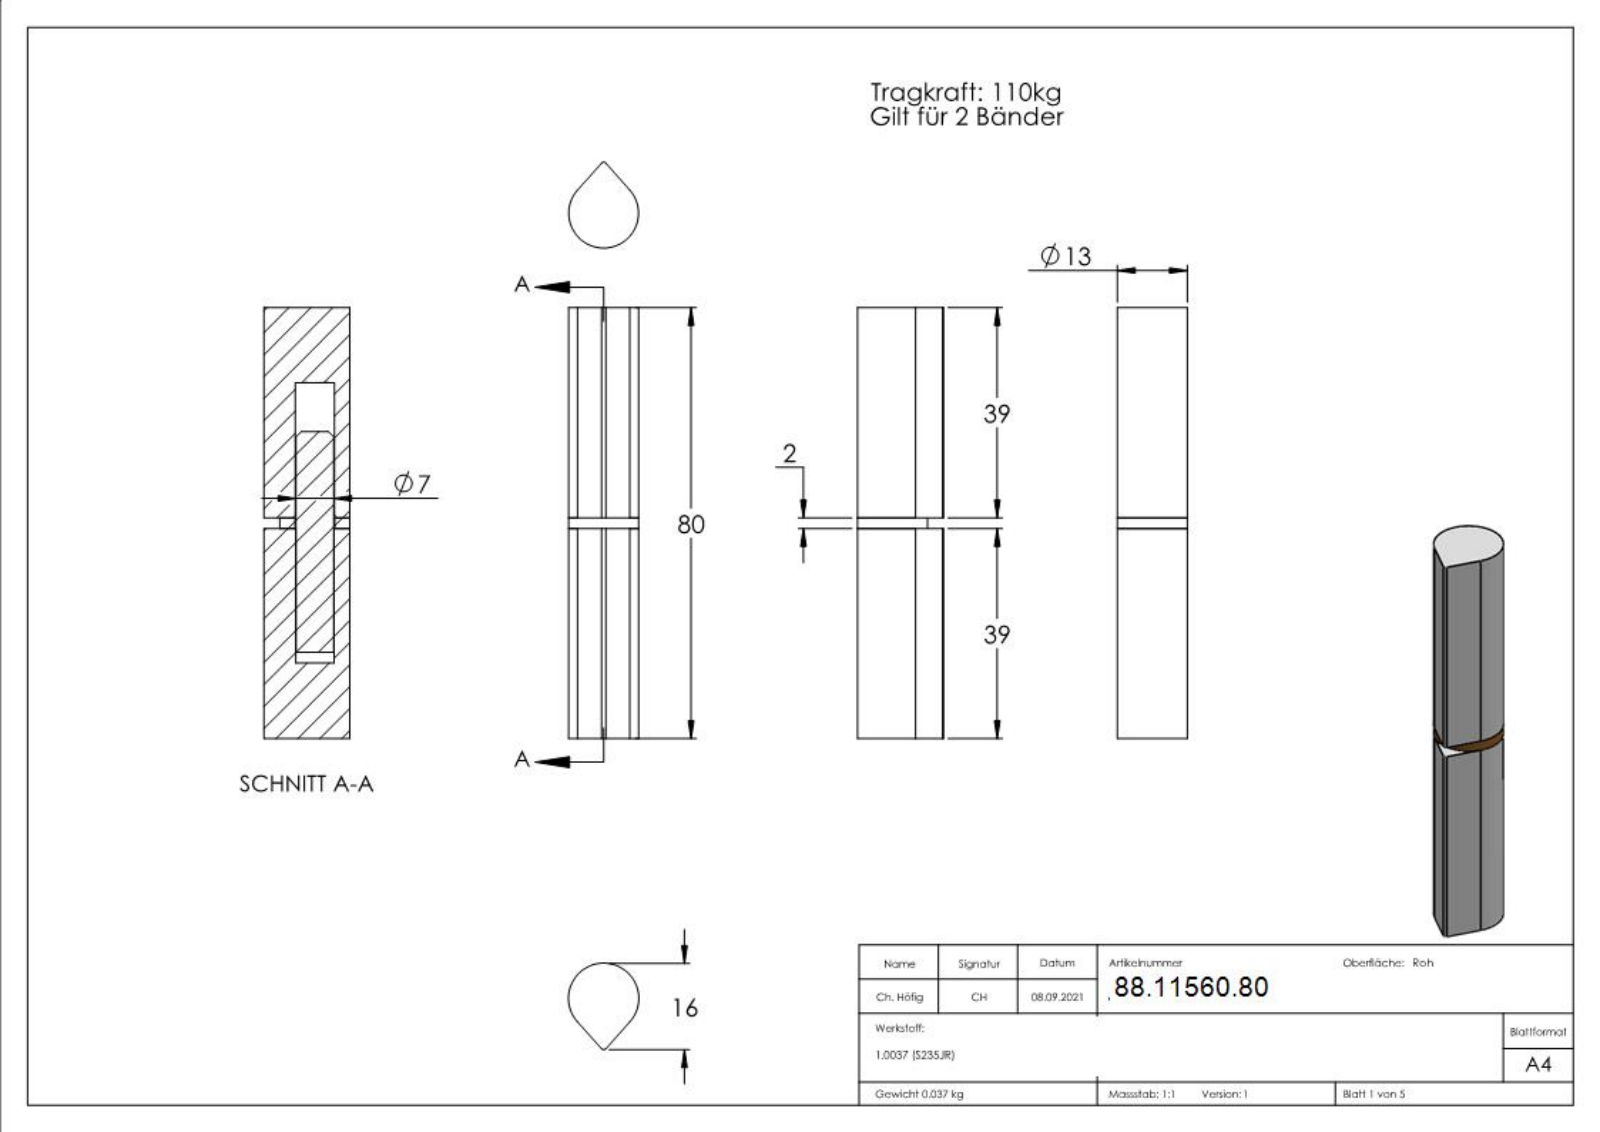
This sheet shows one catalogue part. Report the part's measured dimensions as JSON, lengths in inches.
{"part_name": "560-xx Teil1; 560-80; 560-xx Teil2_560-80 Teil2; 560-xx Teil3 (+3 more)", "step_written_by": "SolidWorks 2018 (CONFIG_CONTROL_DESIGN)", "units": "inches", "bodies": {"solids": 4, "faces": 257, "planar": 126, "cylindrical": 9, "other": 122}, "overall_size": [3.15, 0.63, 0.512], "volume_in3": 0.67, "surface_area_in2": 9.951, "round_holes": [[0.28, 1], [0.285, 1], [0.291, 1]], "round_bosses_or_shafts": [[0.512, 1], [0.276, 1]], "partial_cylinders_radius": [[0.02, 1]], "face_to_face_distances": [1.614, 1.535, 0.079, 3.15, 0.984, 0.551, 2.598, 1.063, 0.63, 0.906]}
